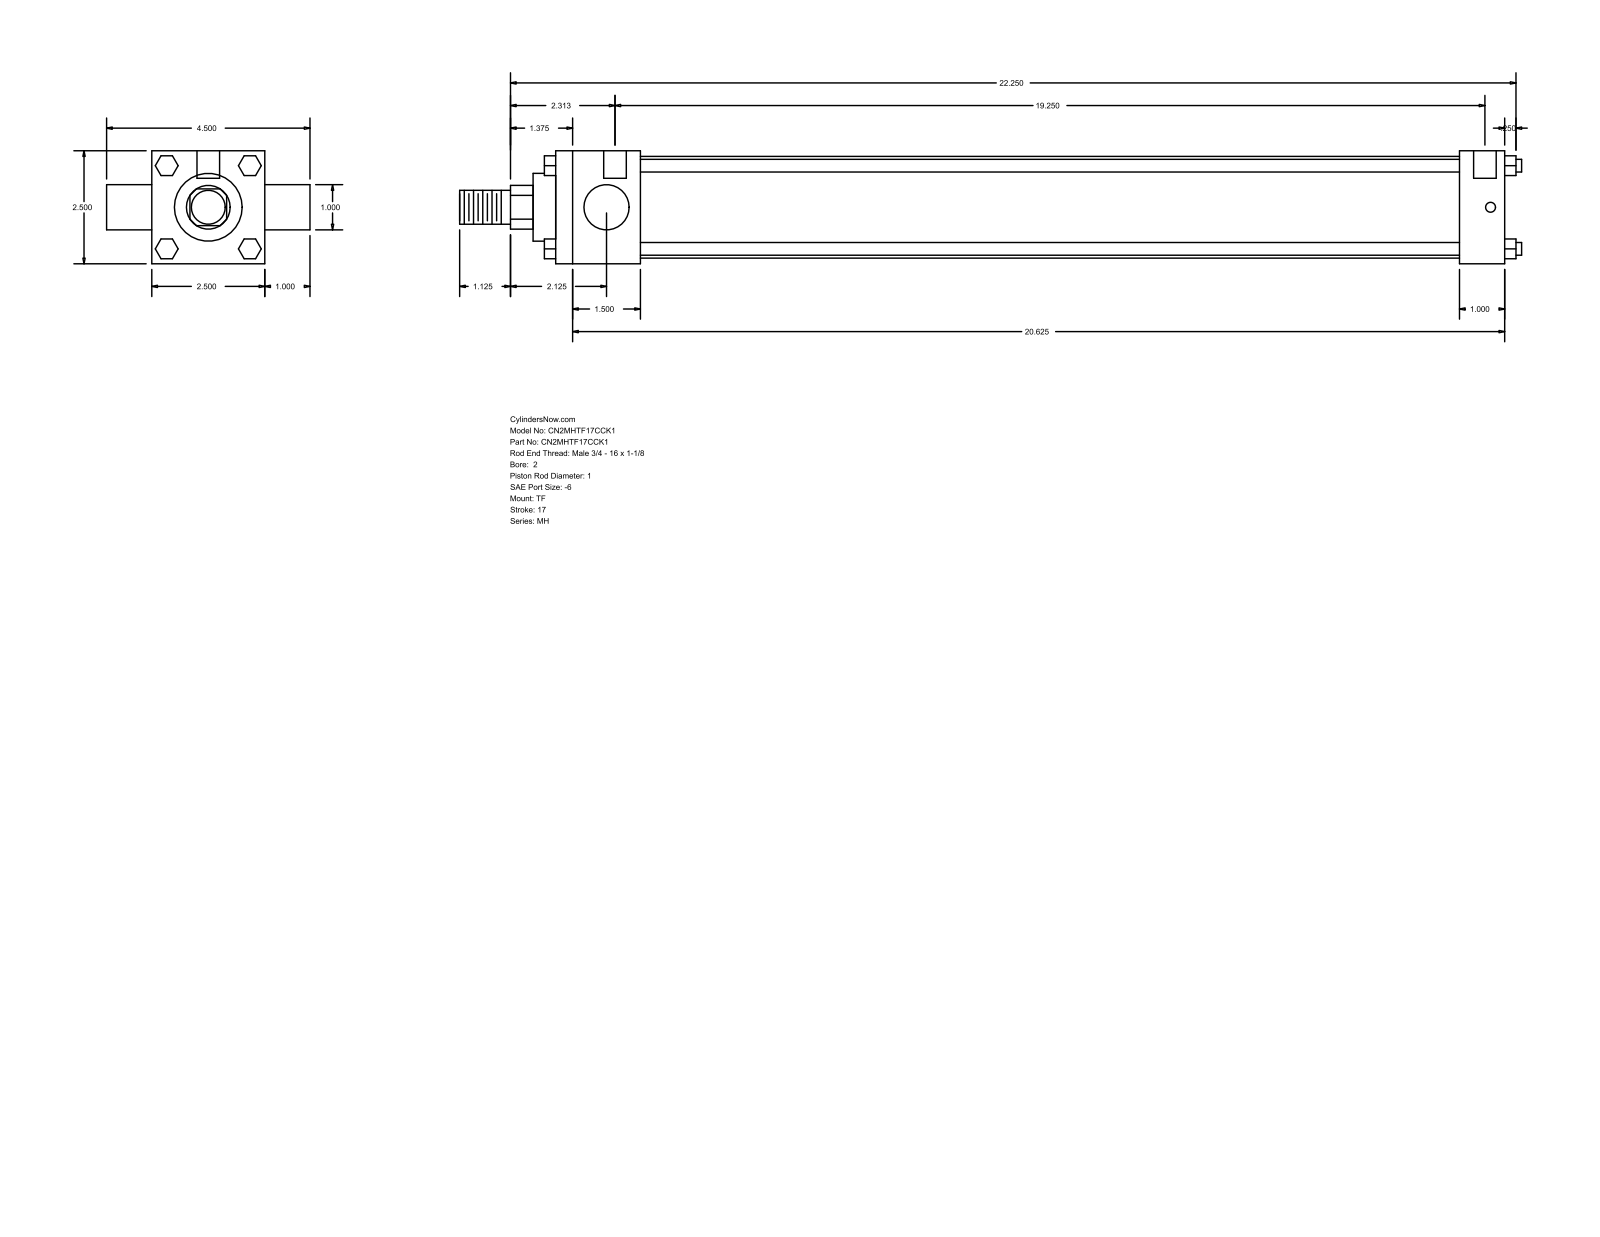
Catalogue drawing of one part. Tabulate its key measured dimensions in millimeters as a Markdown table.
| quantity | value |
| --- | --- |
| part name | MH_TF__0200_1 |
| STEP written by | GSSL Pune (CONFIG_CONTROL_DESIGN) |
| units | millimeters |
| bodies | 0 solids, 120 faces (92 planar, 28 cylindrical, 0 other) |
| overall size | 596.9 × 114.3 × 63.5 |
| round holes (diameter × count) | 5.56 × 3, 12.7 × 2 |
| round bosses / shafts (diameter × count) | 7.14 × 4, 25.4 × 2, 57.15 × 1, 38.1 × 1, 19.05 × 1 |
| partial cylindrical surfaces (radius × count) | 12.29 × 1 |
| main face-to-face distances | 63.5, 533.4, 25.4, 47.63, 508, 460.37, 485.77, 88.9, 546.1, 6.35 |
| hole center spacings | 3.17, 4.76, 488.95, 492.12, 493.71, 496.88 |
